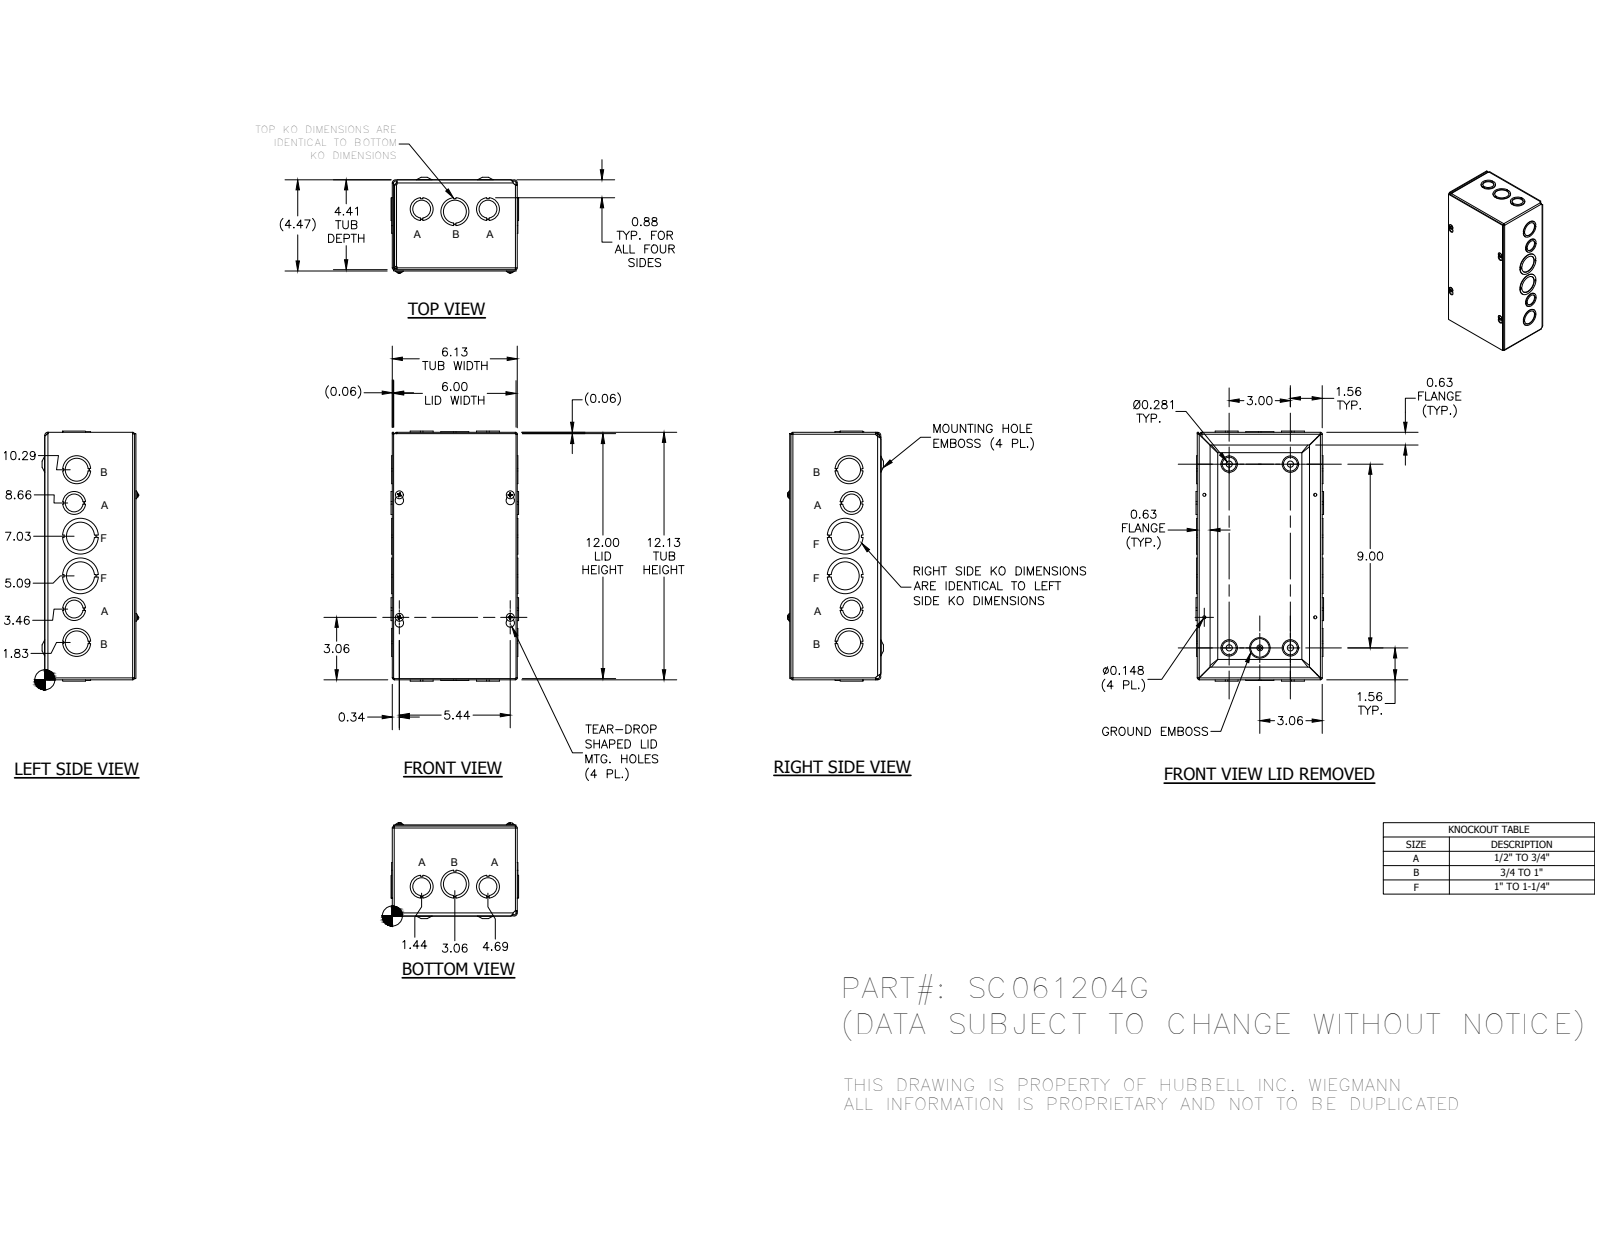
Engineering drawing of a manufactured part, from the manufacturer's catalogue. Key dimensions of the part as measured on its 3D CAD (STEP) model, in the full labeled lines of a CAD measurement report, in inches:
Part name (STEP PRODUCT): SC0612GBKP; SC061204GWRA; SC0612GLID; 34056 (+1 more)
STEP written by: Autodesk Inventor 2014 (AUTOMOTIVE_DESIGN)
Units: inches
Bodies: 22 solids, 862 faces (530 planar, 181 cylindrical, 151 other)
Overall size (bounding box): 12.249 × 6.249 × 4.693
Round holes (diameter × count): ⌀1.125 ×7, ⌀1.375 ×5, ⌀0.148 ×4, ⌀0.3 ×4, ⌀0.875 ×4, ⌀1.75 ×2, ⌀0.165 ×1
Round bosses / shafts (diameter × count): ⌀0.384 ×4, ⌀0.164 ×4, ⌀0.228 ×1
Partial cylindrical surfaces — rounded edges, fillets, slot ends (radius × count): R0.031 ×8, R0.093 ×8, R0.055 ×4, R0.062 ×4, R0.094 ×4, R0.11 ×4, R0.117 ×4, R0.124 ×4
Main face-to-face distances: 0.062, 4.343, 6.063, 4.405, 0.063, 4.406, 4.468, 6.125, 0.062, 6.001
Hole centre spacings: 1.933, 7.598, 8.605, 1.5, 1.635, 1.659, 3, 3.265
